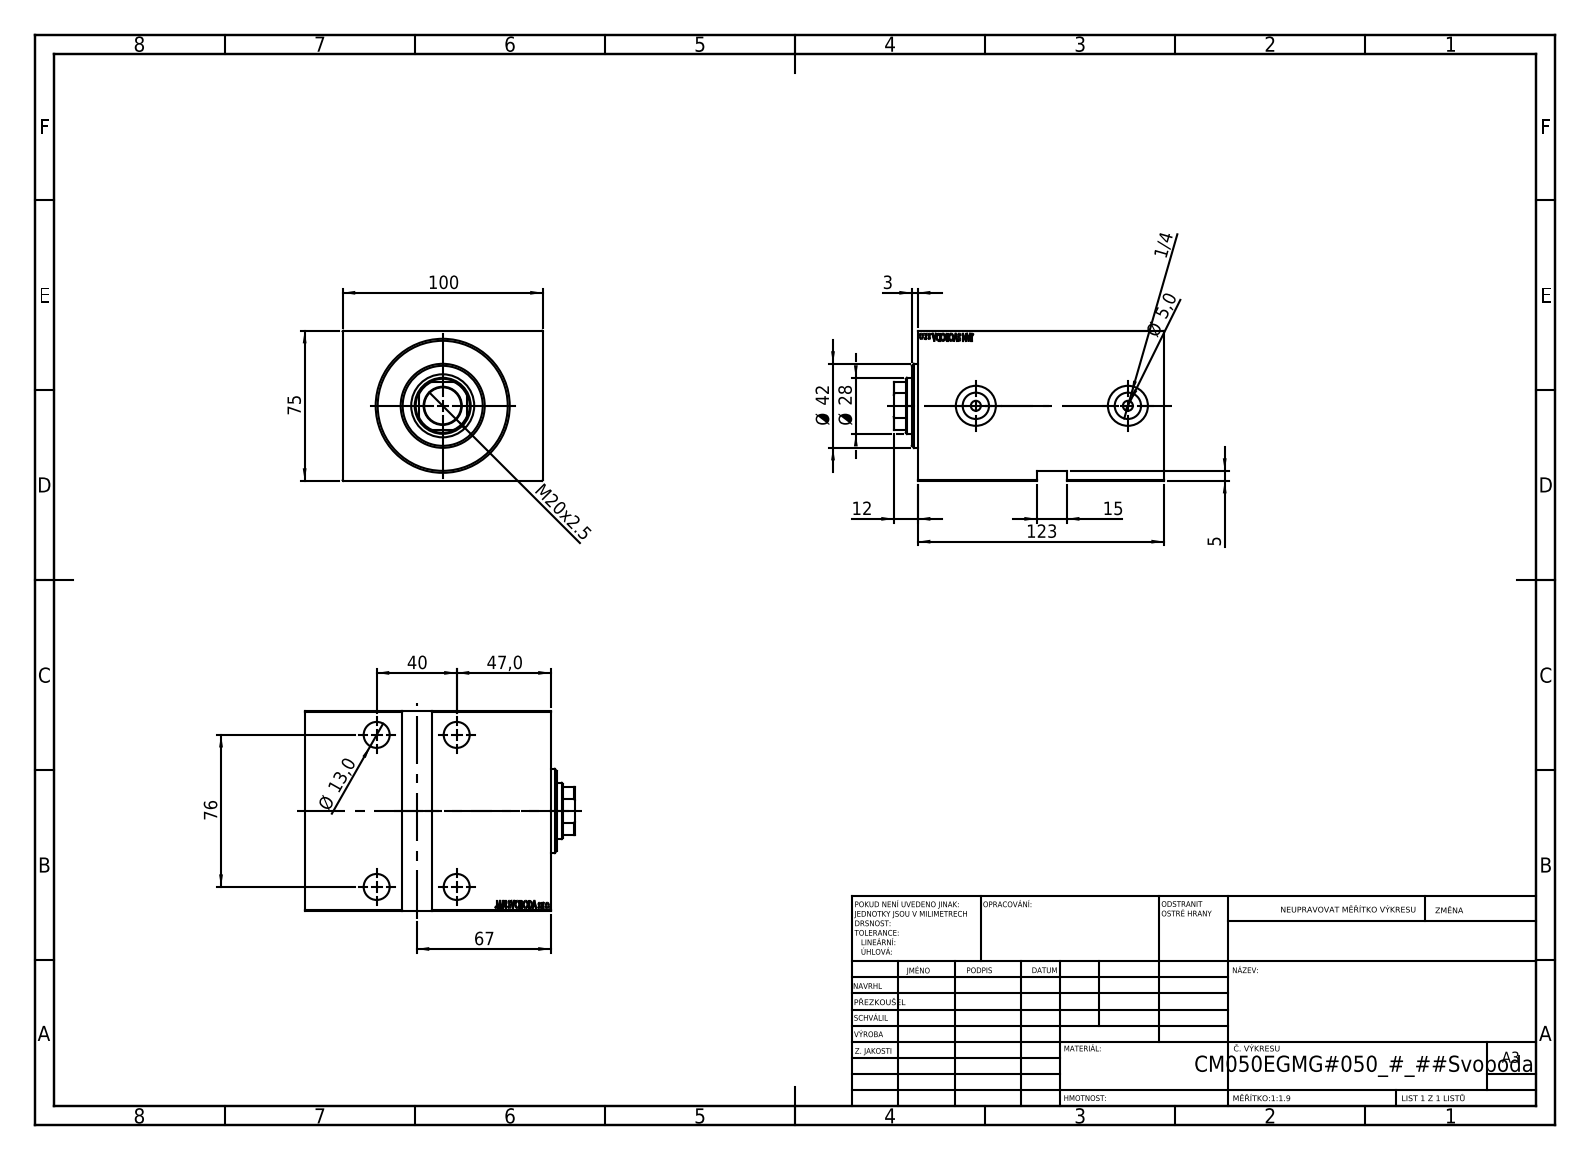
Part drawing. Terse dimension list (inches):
name: V450CM_E_Body; V450CM_E_VCP; V450CM_VC_B
written by: SolidWorks 2019 (CONFIG_CONTROL_DESIGN)
unit: in
bodies: 3 solids, 858 faces (412 planar, 52 cylindrical, 394 other)
size: 5.315 × 3.937 × 2.953
volume: 48.83 in³; area: 186 in²
holes: 4× ⌀0.512, 4× ⌀0.748, 2× ⌀0.197, 2× ⌀0.518, 2× ⌀0.787, 1× ⌀0.728, 1× ⌀1.102, 1× ⌀1.24, 1× ⌀1.969, 1× ⌀2.559
bosses: 1× ⌀2.047, 1× ⌀1.654
rounds: 1× R0.531
face distances: 2.953, 3.937, 4.843, 0.197, 0.551, 4.291, 4.646, 4.094, 2.402, 4.189
hole spacings: 2.992, 1.575, 3.381
